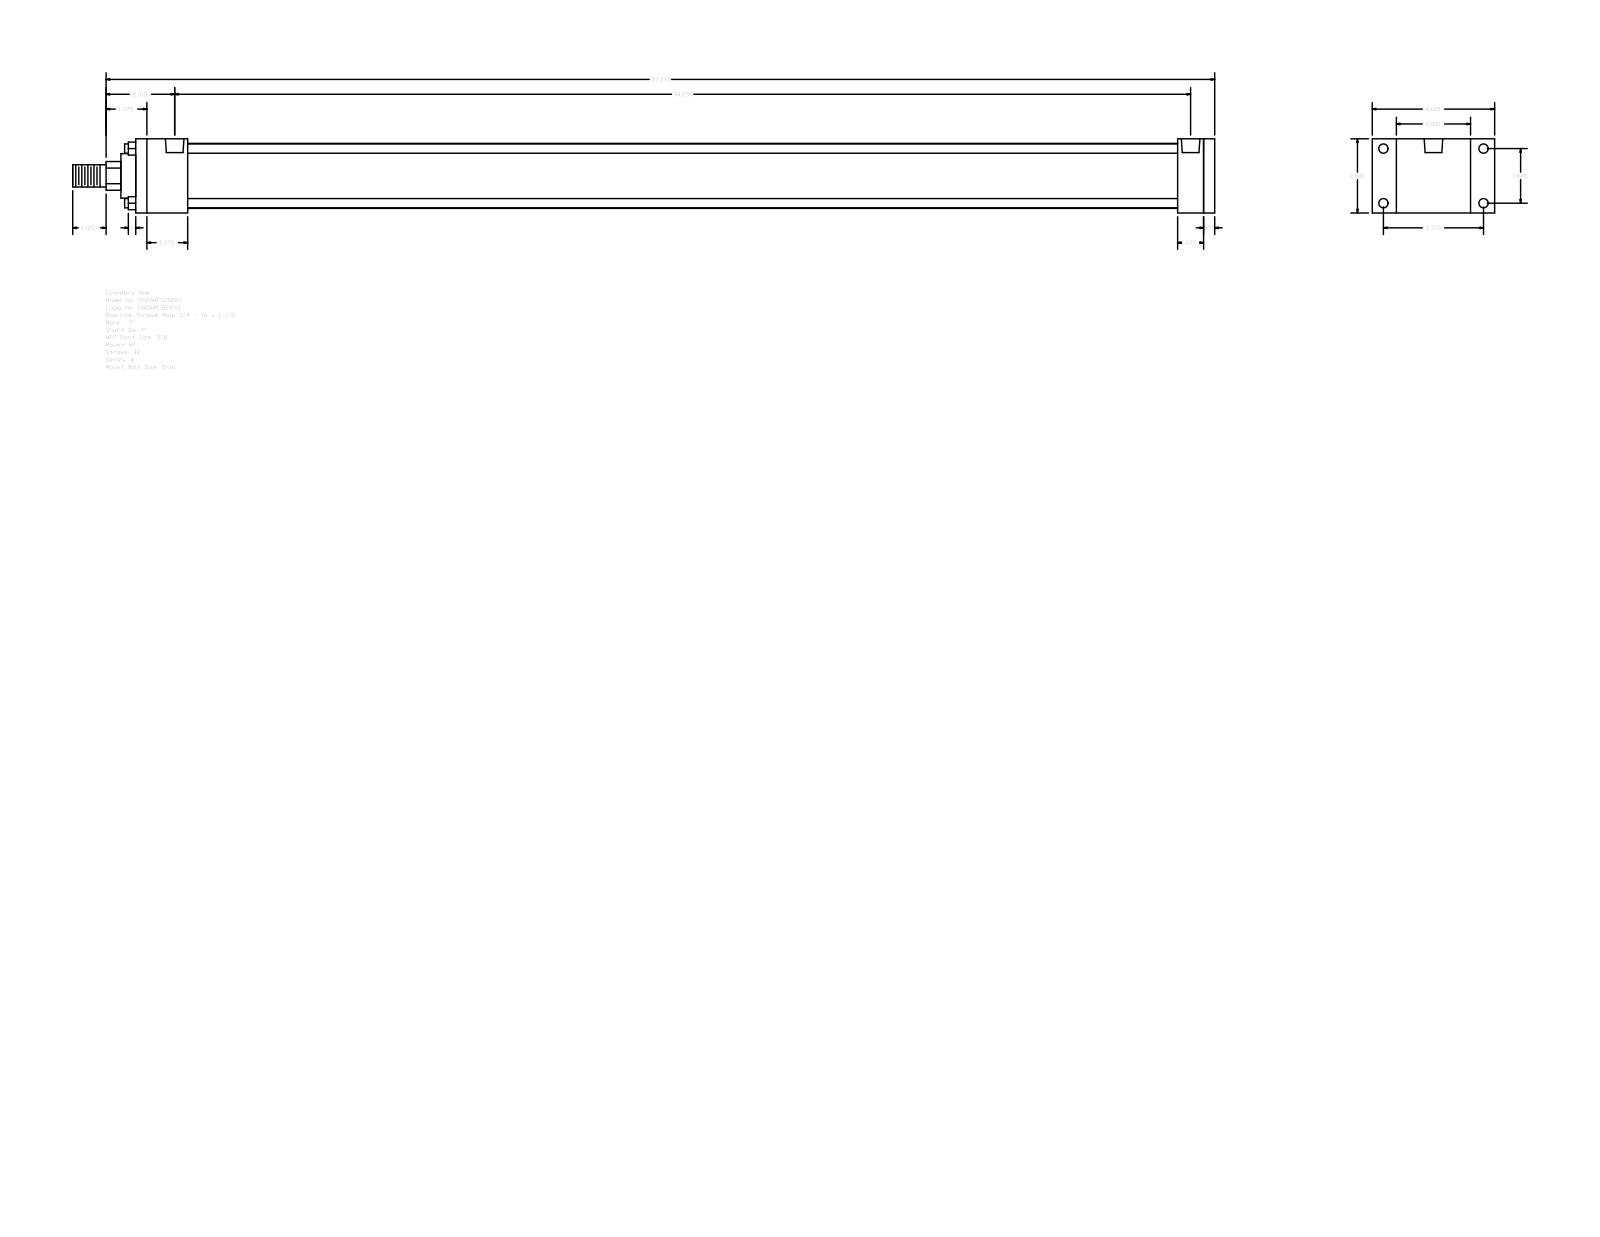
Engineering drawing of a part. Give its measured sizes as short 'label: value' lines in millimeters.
name: A_RF__0200_1
written by: GSSL Pune (CONFIG_CONTROL_DESIGN)
unit: mm
bodies: 0 solids, 92 faces (64 planar, 28 cylindrical, 0 other)
size: 977.9 × 104.78 × 63.5
holes: 4× ⌀5.56, 4× ⌀7.94, 2× ⌀15.93
bosses: 4× ⌀7.94, 1× ⌀55.63, 1× ⌀38.1, 1× ⌀25.4, 1× ⌀19.05
rounds: 1× R12.29
face distances: 63.5, 9.53, 923.93, 914.4, 44.45, 20.64, 869.95, 879.48, 892.18, 847.73
hole spacings: 46.74, 85.72, 97.63, 864.38, 1.59, 3.98, 865.97, 868.36
